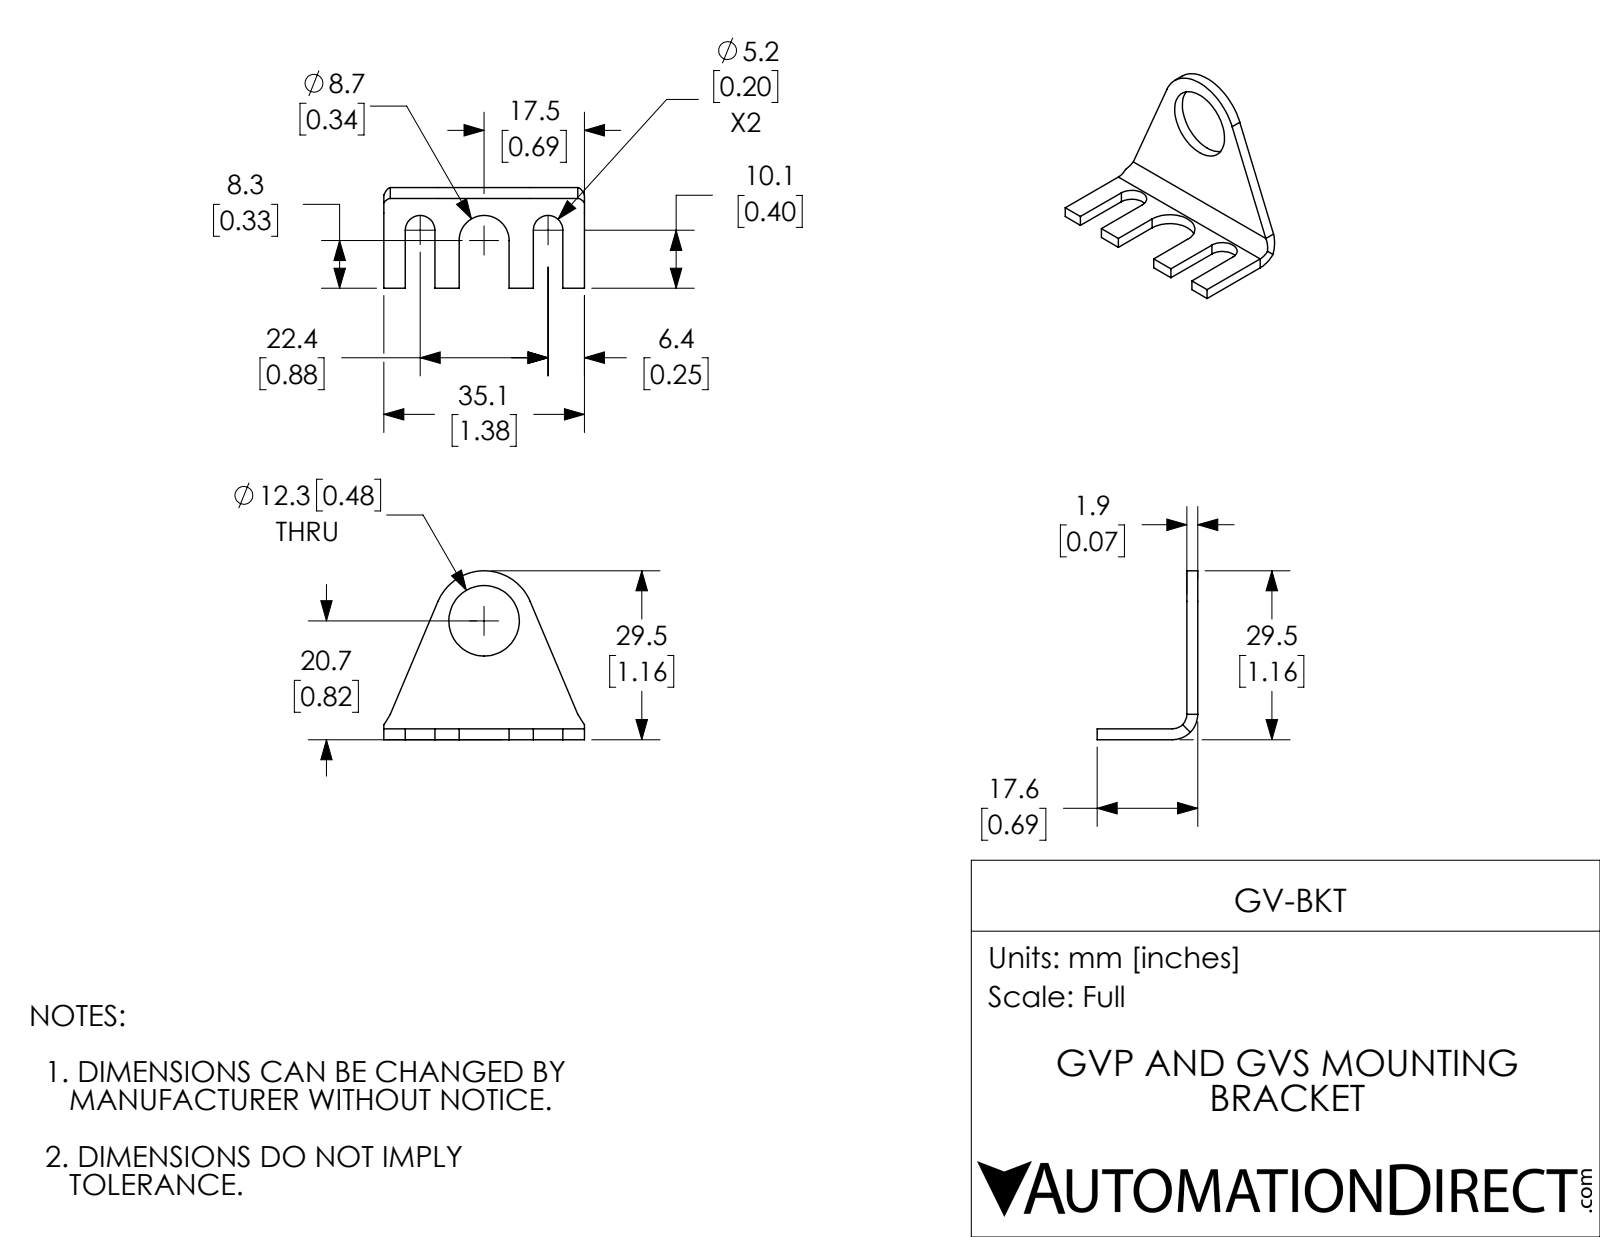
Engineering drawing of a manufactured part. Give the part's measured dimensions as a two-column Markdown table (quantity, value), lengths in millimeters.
| quantity | value |
| --- | --- |
| part name | GV-BKT |
| STEP written by | SolidWorks 2018 (AUTOMOTIVE_DESIGN) |
| units | millimeters |
| bodies | 1 solid, 30 faces (20 planar, 8 cylindrical, 2 other) |
| overall size | 35.1 × 29.5 × 17.6 |
| volume | 1 600 mm³ |
| surface area | 2 152 mm² |
| round holes (diameter × count) | 12.3 × 1 |
| partial cylindrical surfaces (radius × count) | 2.6 × 2, 2.5 × 1, 4.4 × 1, 4.4 × 1, 8.7 × 1 |
| main face-to-face distances | 1.9, 8.9, 26.1, 3.8, 31.3, 5.2, 22.4, 13.2, 21.9, 9.4 |
